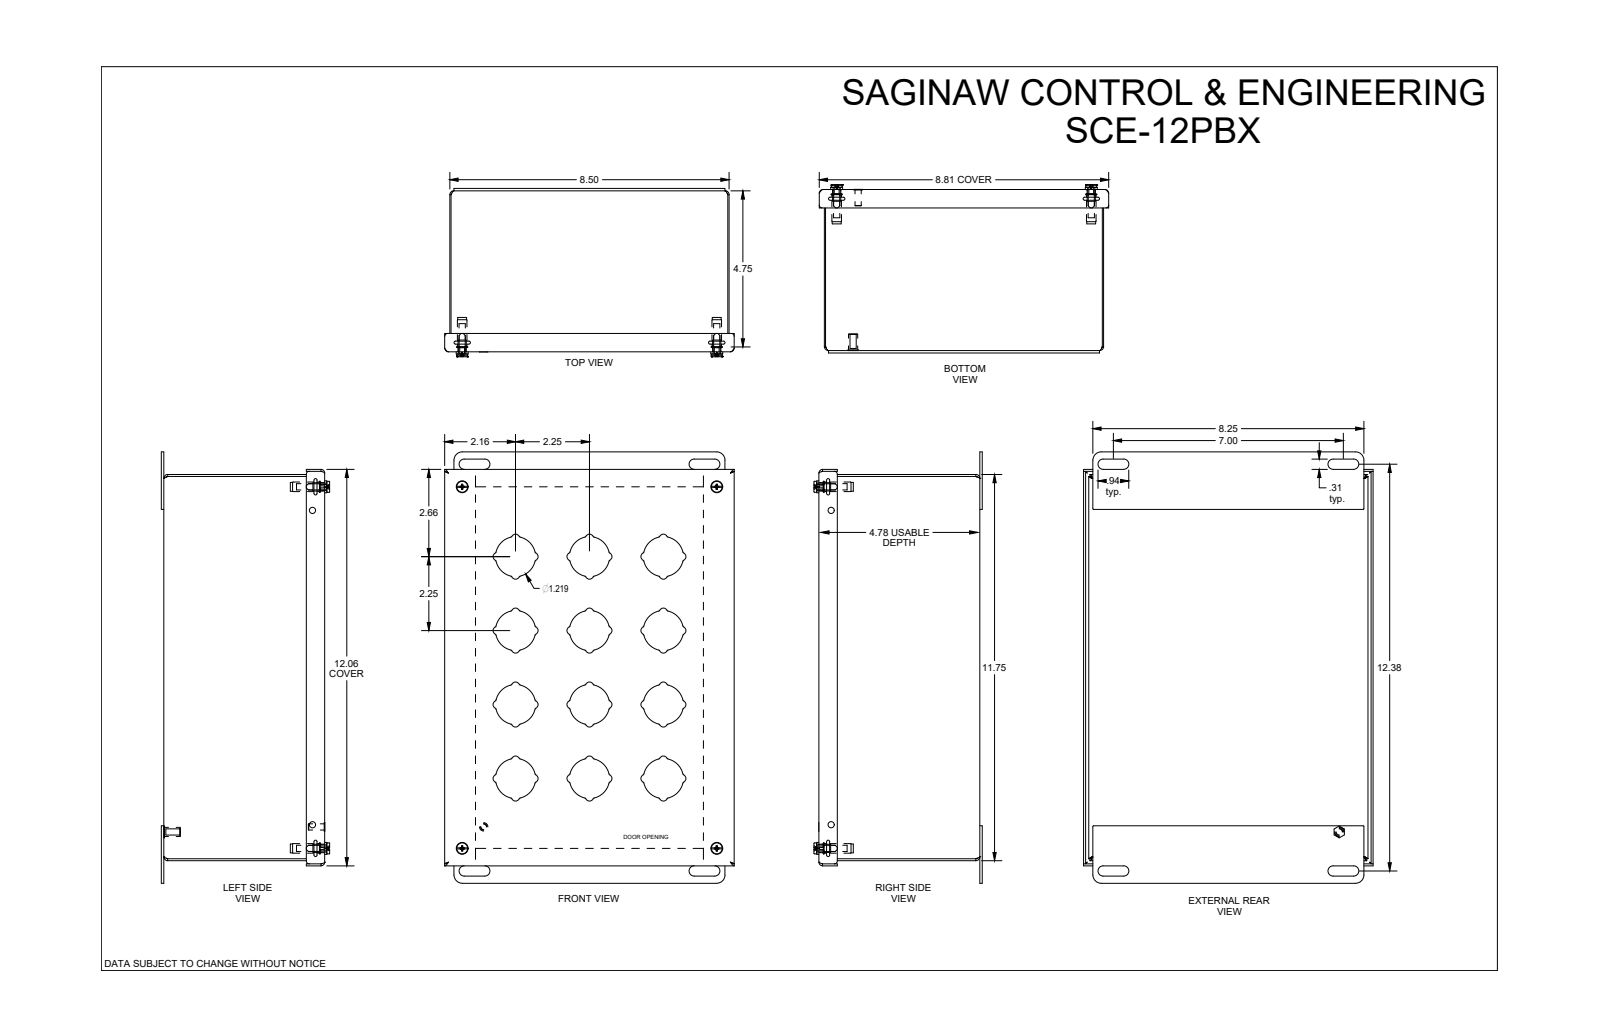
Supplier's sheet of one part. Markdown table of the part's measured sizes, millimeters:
| quantity | value |
| --- | --- |
| part name | SCE-12PBX |
| STEP written by | SolidWorks 2019 (AUTOMOTIVE_DESIGN) |
| units | millimeters |
| bodies | 15 solids, 612 faces (166 planar, 370 cylindrical, 76 other) |
| overall size | 333.4 × 223.9 × 127.4 |
| volume | 465 100 mm³ |
| surface area | 607 000 mm² |
| round holes (diameter × count) | 4.8 × 5, 5.6 × 4, 6.4 × 4, 6.8 × 4, 8.1 × 4, 4.9 × 1, 7.1 × 1 |
| round bosses / shafts (diameter × count) | 11.1 × 4, 9.2 × 4, 8.6 × 4, 7.4 × 4, 6.9 × 4, 6.6 × 4, 7.1 × 1, 6.5 × 1 |
| partial cylindrical surfaces (radius × count) | 1 × 96, 3.2 × 48, 1.5 × 20, 15.5 × 12, 0.4 × 8, 2.9 × 8, 4 × 8, 6.2 × 8 |
| main face-to-face distances | 1.5, 124, 214.4, 122.4, 125.5, 296.9, 215.9, 212.9, 119.1, 4.8 |
| hole center spacings | 279.4, 279.4, 197, 341.9, 196.9, 196.9, 341.8, 341.8 |
